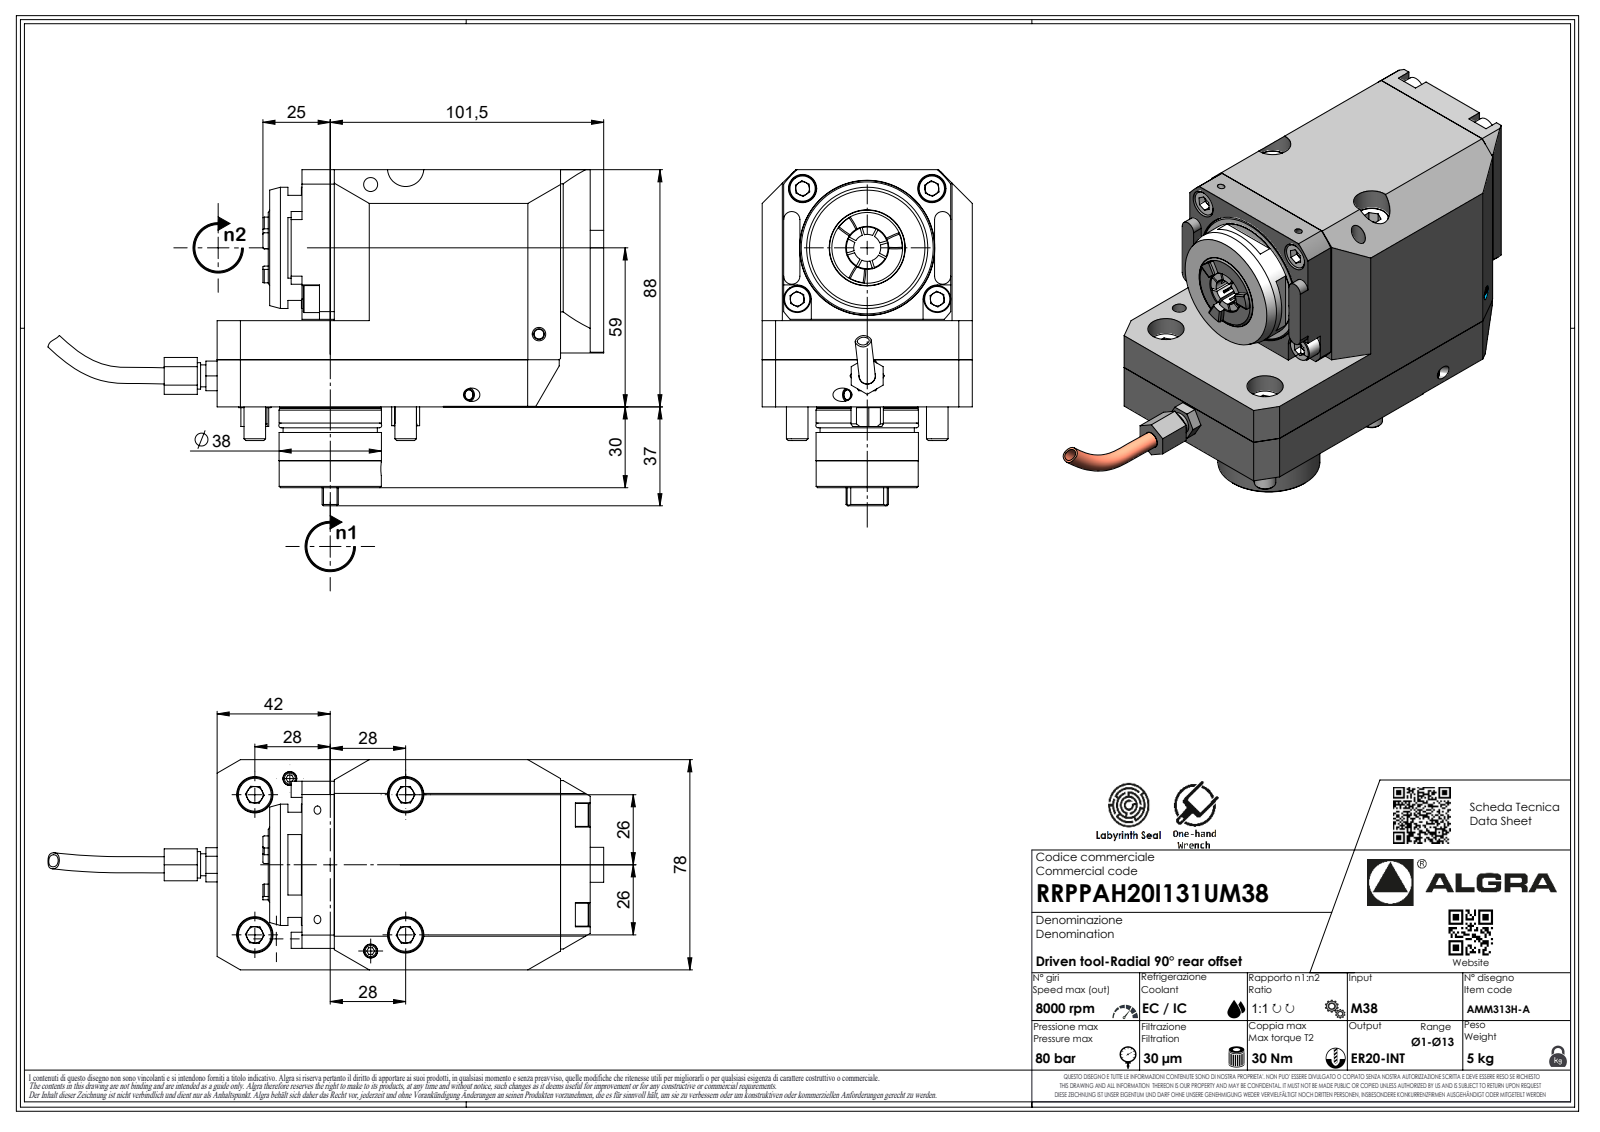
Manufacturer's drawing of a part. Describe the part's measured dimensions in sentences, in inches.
The part is named "RRPPAH20I131UM38". Its 3-D file was written by "SolidWorks 2023 (AUTOMOTIVE_DESIGN)". It is 1 solid with 476 faces: 317 planar, 52 cylindrical and 107 other. Overall it measures 5.65 by 4.909 by 3.071 inches. Its volume is 48.36 cubic inches and its surface area 92.98 square inches. Round holes: 1 of diameter 0.083. Round bosses or shafts: 1 of diameter 1.772, 1 of diameter 1.496, 1 of diameter 1.492, 1 of diameter 1.48, 1 of diameter 1.378, 1 of diameter 0.472, 1 of diameter 0.251, 1 of diameter 0.067. Partial cylindrical surfaces (rounded edges, fillets, slot ends): 7 of radius 0.013, 7 of radius 0.02, 7 of radius 0.146, 4 of radius 0.118, 1 of radius 0.008, 1 of radius 0.236, 1 of radius 0.256, 1 of radius 0.309. The main face-to-face distances are 3.071, 3.465, 2.205, 1.26, 1.252, 3.457, 5.453, 0.768, 0.472, 1.24.
